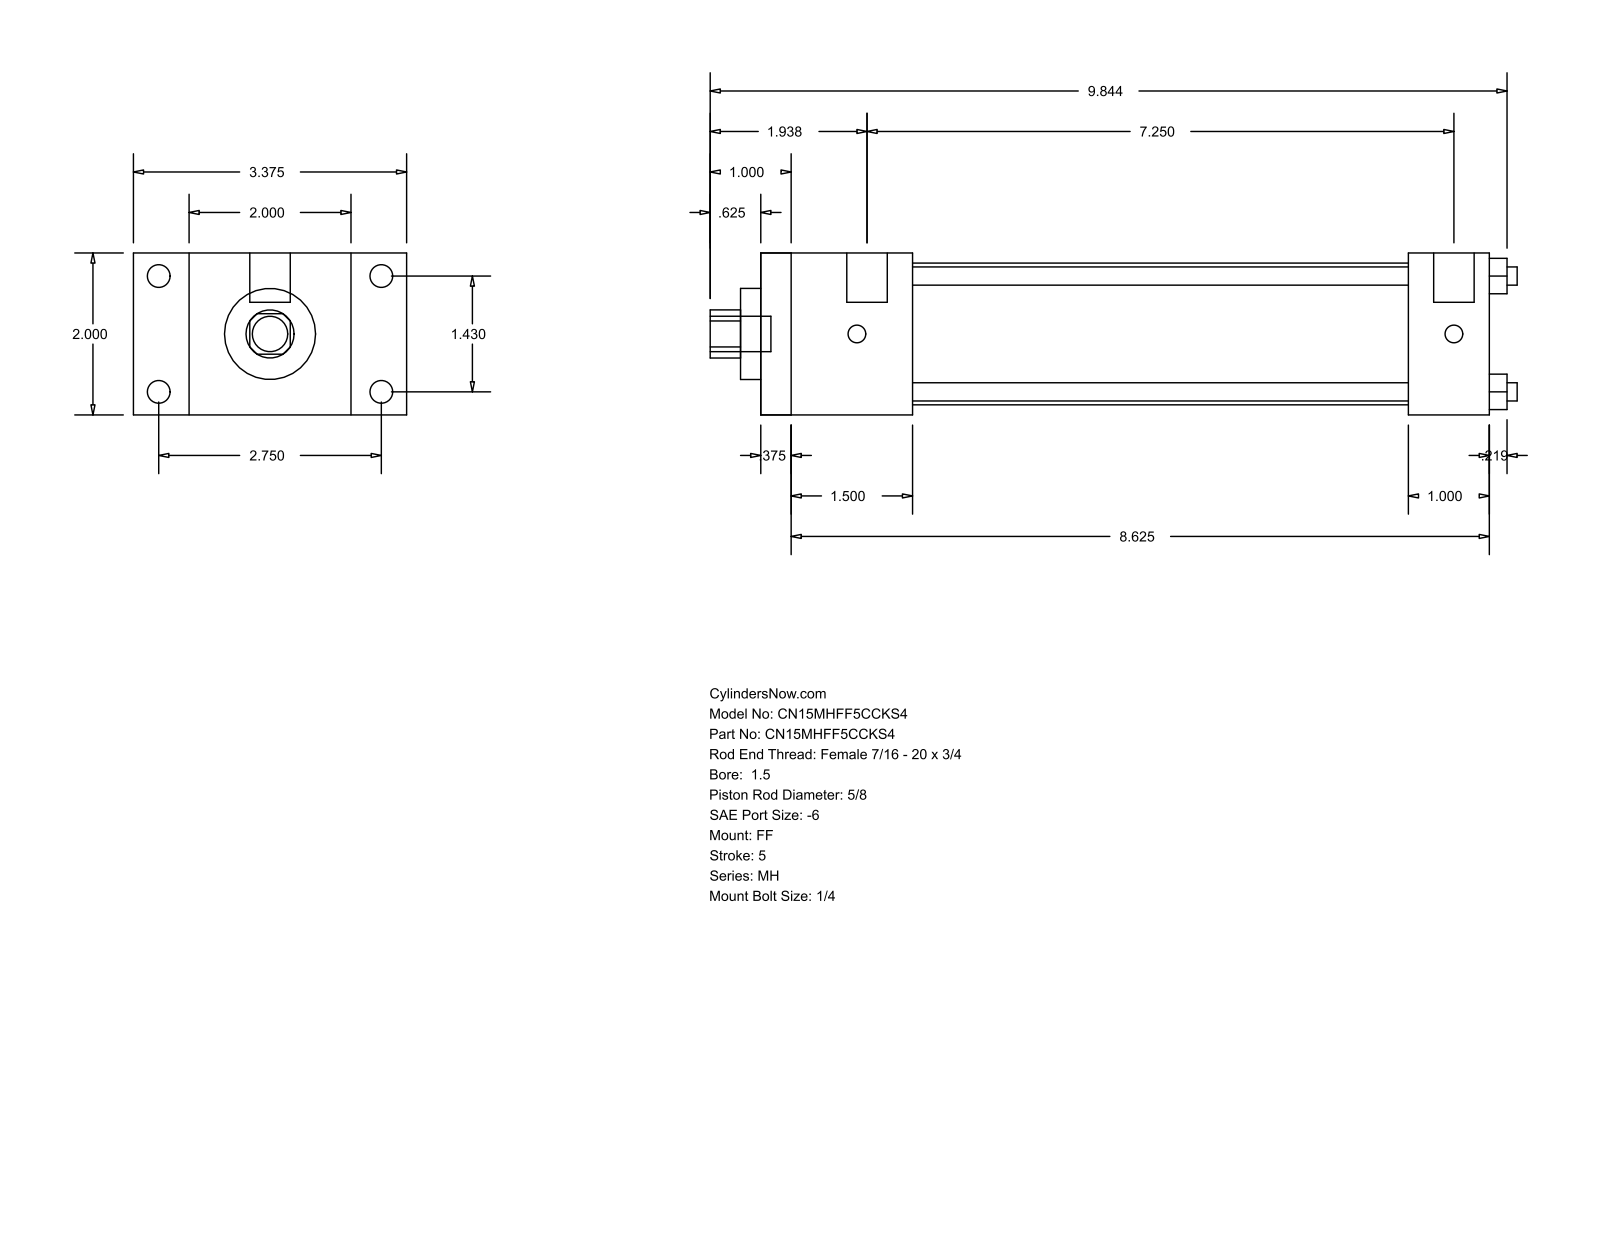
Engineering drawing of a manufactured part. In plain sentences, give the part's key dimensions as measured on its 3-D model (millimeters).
The part is named "MH_FF__0150_0.625". Its 3-D file was written by "GSSL Pune (CONFIG_CONTROL_DESIGN)". It is 0 solids with 92 faces: 64 planar, 28 cylindrical and 0 other. Overall it measures 253.21 by 85.72 by 50.8 millimeters. Round holes: 4 of diameter 5.71, 1 of diameter 15.88, 1 of diameter 28.57, 1 of diameter 44.45. Round bosses or shafts: 4 of diameter 7.14, 4 of diameter 5.56, 2 of diameter 12.7, 1 of diameter 11.11. Partial cylindrical surfaces (rounded edges, fillets, slot ends): 1 of radius 7.54. The main face-to-face distances are 50.8, 228.59, 9.52, 219.07, 25.4, 17.46, 68.26, 47.62, 38.1, 180.97. The hole center spacings are 25.68, 36.32, 51.36.
